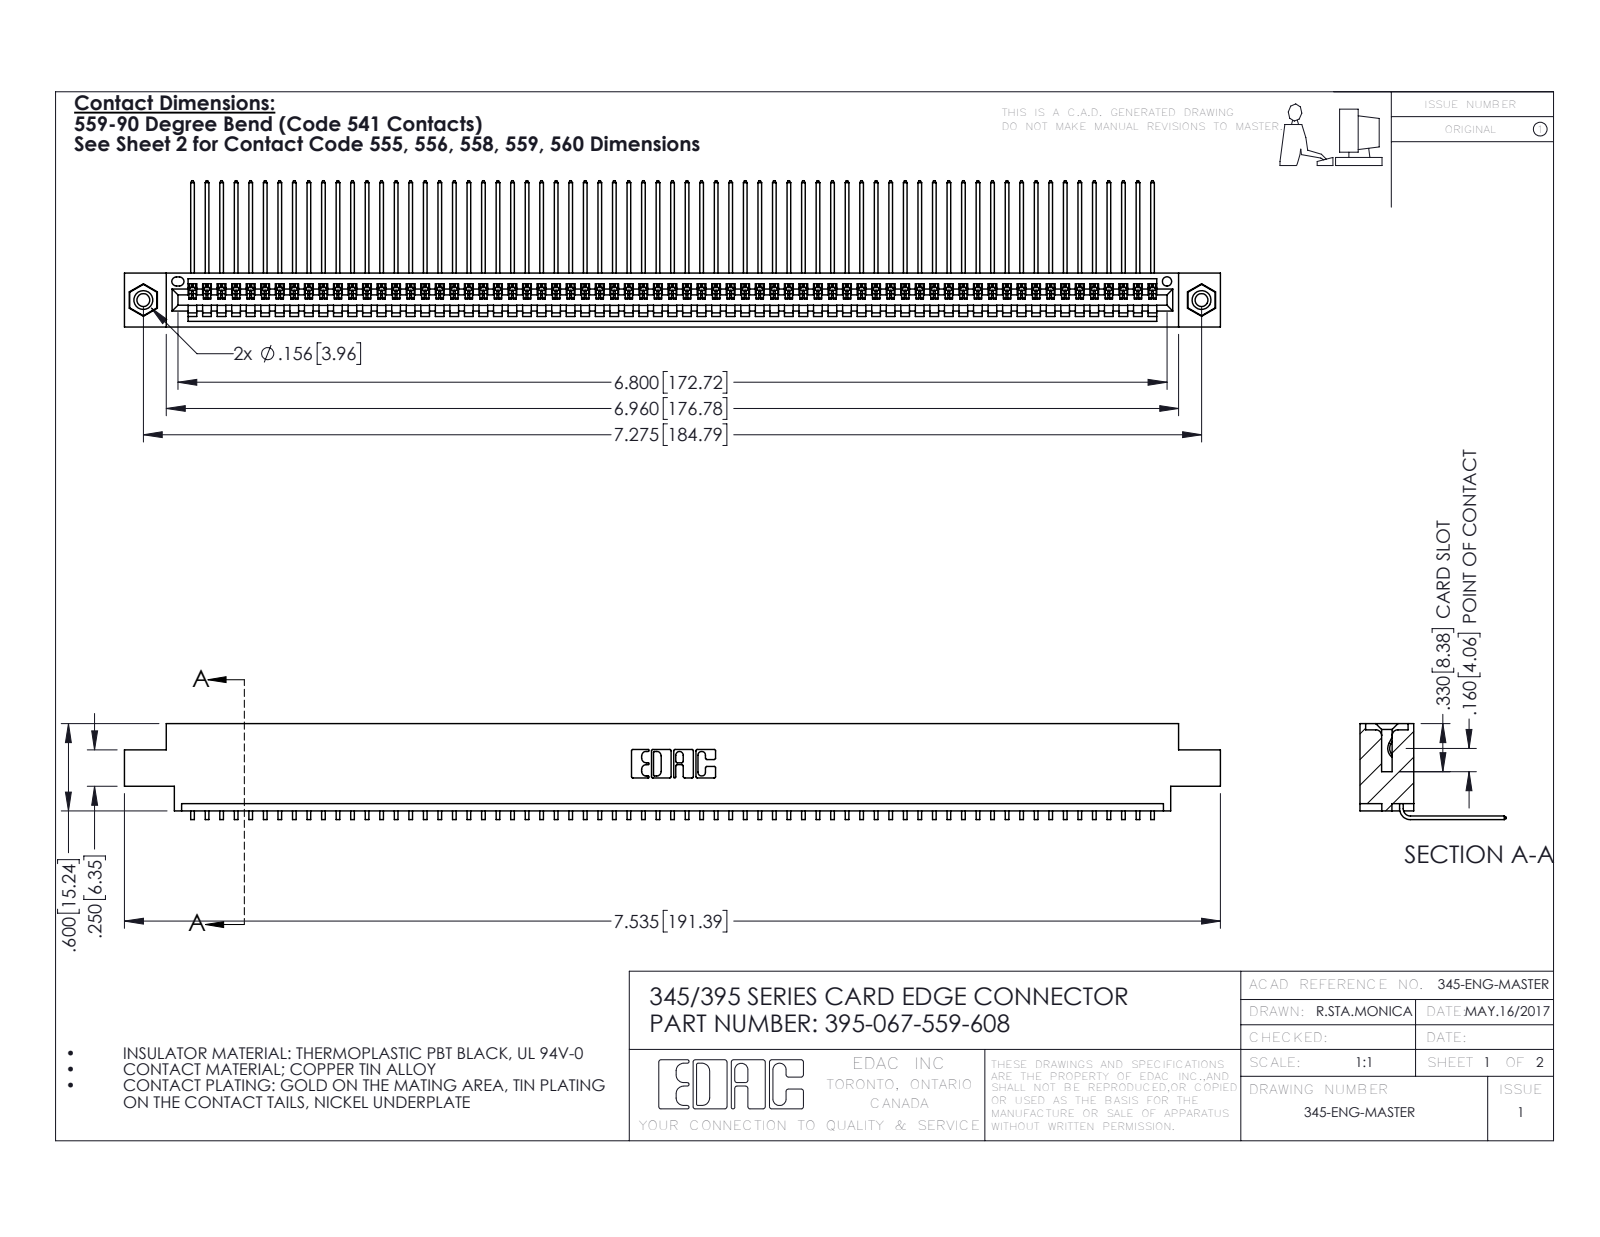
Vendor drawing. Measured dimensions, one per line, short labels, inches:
name: 395-067-559-608; 345-250-001_345-250-003-102; 345-292-001_558 559 Tail - 1; 345 Part_0.170 Offset - 0.156 Dia-TI
written by: SolidWorks 2016 (CONFIG_CONTROL_DESIGN)
unit: in
bodies: 70 solids, 4210 faces (2930 planar, 1264 cylindrical, 16 other)
size: 7.535 × 1.005 × 0.659
volume: 1.128 in³; area: 40.86 in²
holes: 2× ⌀0.089, 2× ⌀0.125, 2× ⌀0.156, 1× ⌀0.064
bosses: 2× ⌀0.155
rounds: 134× R0.006, 22× R0.01, 6× R0.007, 6× R0.031, 3× R0.026, 2× R0.031, 2× R0.04, 1× R0.014
face distances: 0.072, 0.298, 0.37, 0.2, 0.098, 0.272, 0.025, 0.225, 0.175, 0.149
hole spacings: 0.27, 7.039, 7.275
